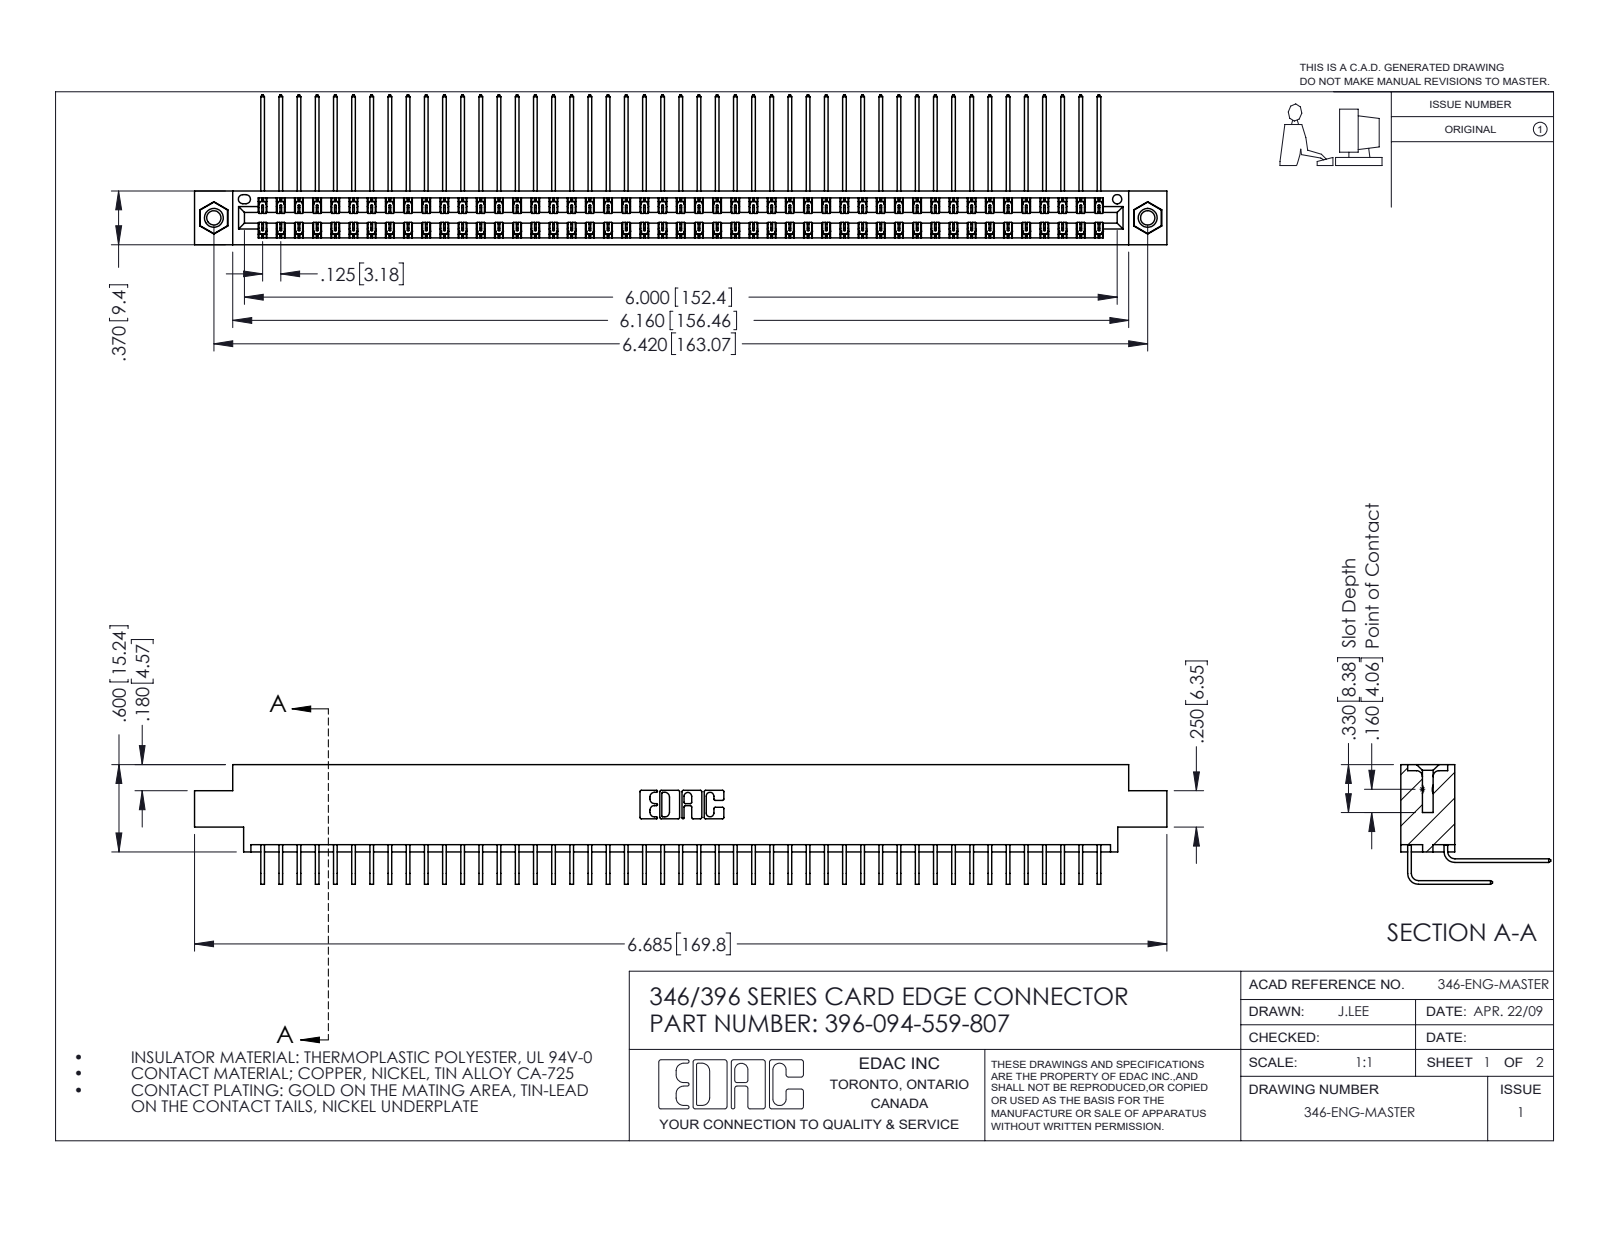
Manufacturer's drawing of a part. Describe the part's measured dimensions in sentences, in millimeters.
The part is named "345-292-001_558 559 Tail - 1; 345-250-001_345-250-005-103; 346 Part_0.170 Offset - 0.156 Dia-TI; 396-094-559-807 (+1 more)". Its 3-D file was written by "SolidWorks 2016 (CONFIG_CONTROL_DESIGN)". It is 97 solids with 5262 faces: 3590 planar, 1656 cylindrical and 16 other. Overall it measures 169.8 by 26.2 by 20.9 millimeters. Its volume is 16 980 cubic millimeters and its surface area 26 220 square millimeters. Round holes: 2 of diameter 2.5, 2 of diameter 3.2, 2 of diameter 4, 1 of diameter 1.6. Round bosses or shafts: 2 of diameter 3.9. Partial cylindrical surfaces (rounded edges, fillets, slot ends): 141 of radius 0.2, 22 of radius 0.3, 6 of radius 0.2, 6 of radius 0.8, 3 of radius 0.7, 2 of radius 0.4, 2 of radius 0.6, 2 of radius 0.6. The main face-to-face distances are 1.2, 8.2, 0.6, 9.4, 6.4, 1.8, 7.6, 7, 5.6, 3.8. The hole center spacings are 6.2, 157.8, 163.1.
